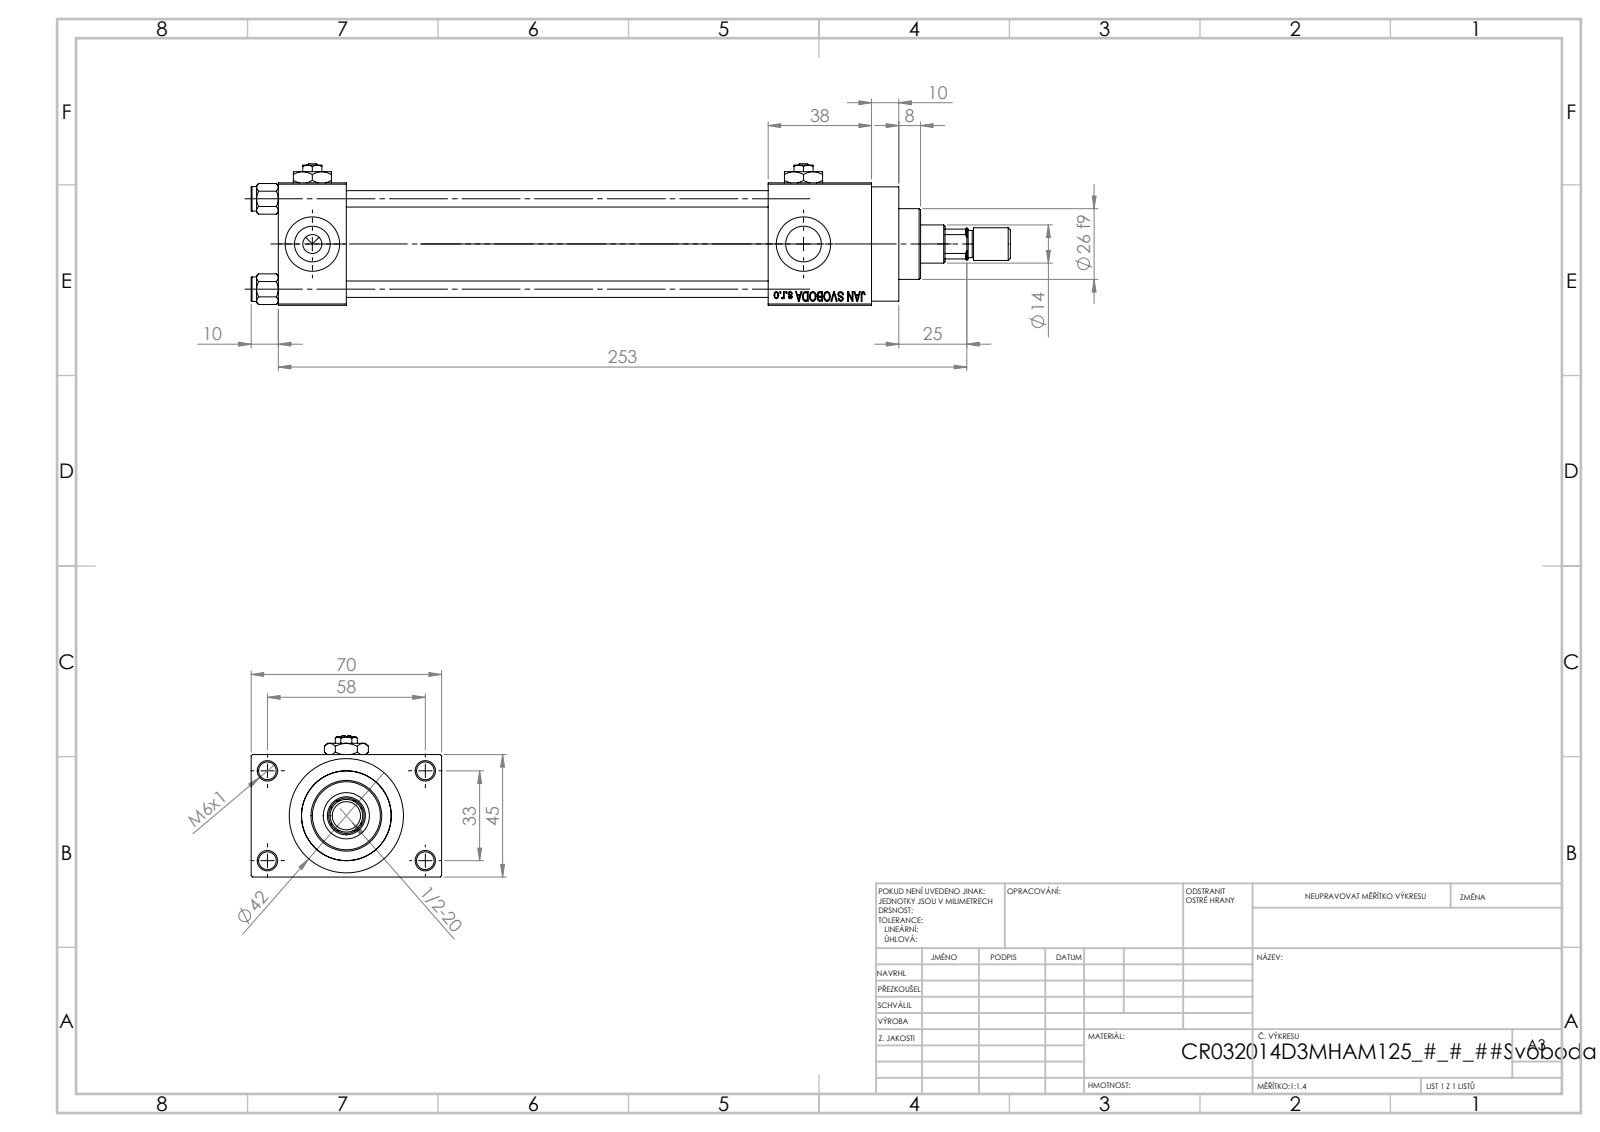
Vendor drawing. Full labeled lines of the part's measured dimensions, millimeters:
Part name (STEP PRODUCT): V215_VC_A; NUT_M5_D; V215CR_D_Body; ROD_END_AH (+3 more)
STEP written by: SolidWorks 2019 (CONFIG_CONTROL_DESIGN)
Units: millimetres
Bodies: 14 solids, 1215 faces (546 planar, 103 cylindrical, 566 other)
Overall size (bounding box): 279 × 70 × 52
Volume: 293 476 mm³ · Surface area: 113 604 mm²
Round holes (diameter × count): ⌀6.5 ×5, ⌀6 ×4, ⌀13.16 ×4, ⌀20 ×4, ⌀7 ×3, ⌀14 ×1, ⌀17 ×1, ⌀24 ×1, ⌀32 ×1, ⌀33 ×1
Round bosses / shafts (diameter × count): ⌀9 ×4, ⌀42 ×1, ⌀38 ×1, ⌀26 ×1, ⌀12 ×1, ⌀10 ×1
Partial cylindrical surfaces — rounded edges, fillets, slot ends (radius × count): R6.5 ×1
Main face-to-face distances: 45, 25, 12.5, 155, 180, 57.5, 193, 38, 218, 70
Hole centre spacings: 12.4, 23.48, 33.2, 33.37, 35.35, 45.6, 56.35, 33
